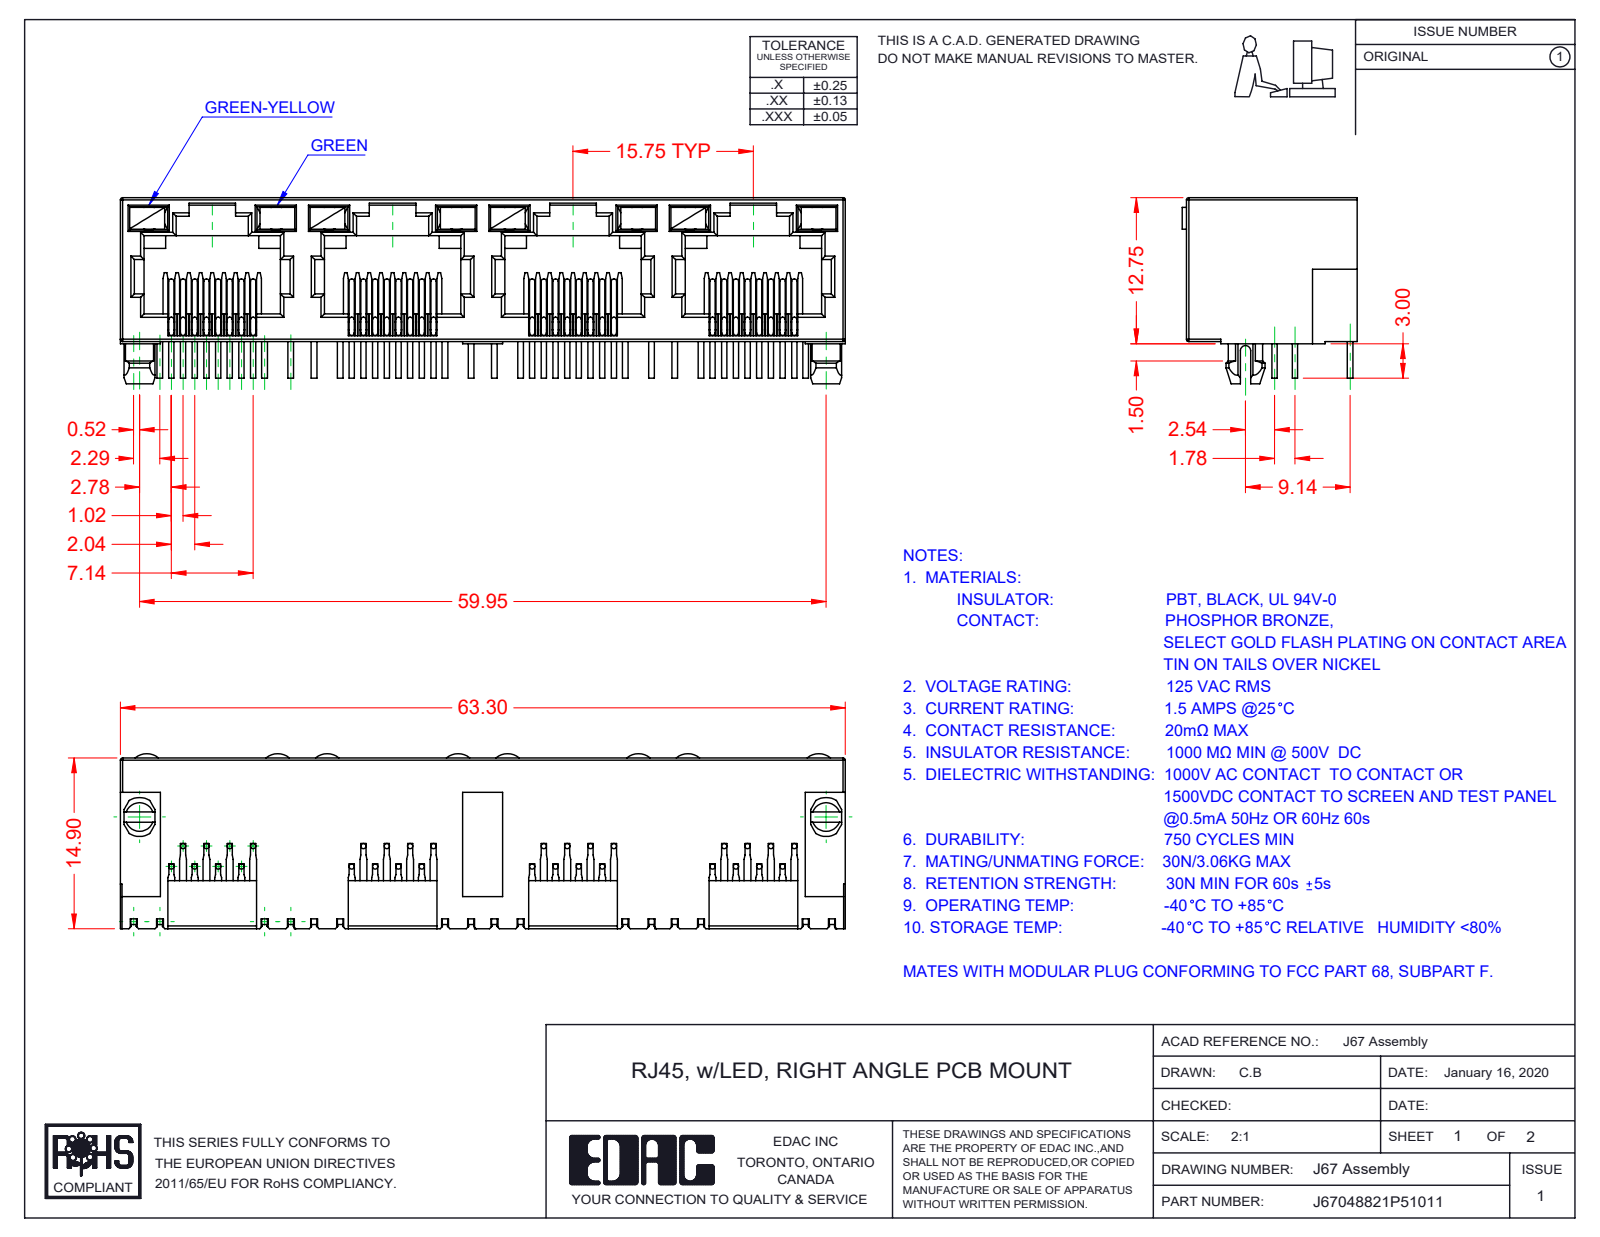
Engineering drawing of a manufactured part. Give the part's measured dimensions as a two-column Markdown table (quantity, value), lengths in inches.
| quantity | value |
| --- | --- |
| part name | 67 LED RH_3-Green; 67 Contacts; 67 Insulator; J67048822P53011 (+1 more) |
| STEP written by | SolidWorks 2016 (CONFIG_CONTROL_DESIGN) |
| units | inches |
| bodies | 41 solids, 2473 faces (1781 planar, 484 cylindrical, 208 other) |
| overall size | 2.492 × 0.64 × 0.602 |
| volume | 0.315 in³ |
| surface area | 17.94 in² |
| round bosses / shafts (diameter × count) | 0.018 × 96 |
| partial cylindrical surfaces (radius × count) | 0.008 × 66, 0.012 × 29, 0.018 × 9, 0.061 × 8, 0.059 × 2, 0.067 × 2, 0.014 × 1, 0.039 × 1 |
| main face-to-face distances | 0.02, 0.494, 0.074, 0.035, 0.394, 0.62, 0.039, 0.055, 0.433, 0.468 |
